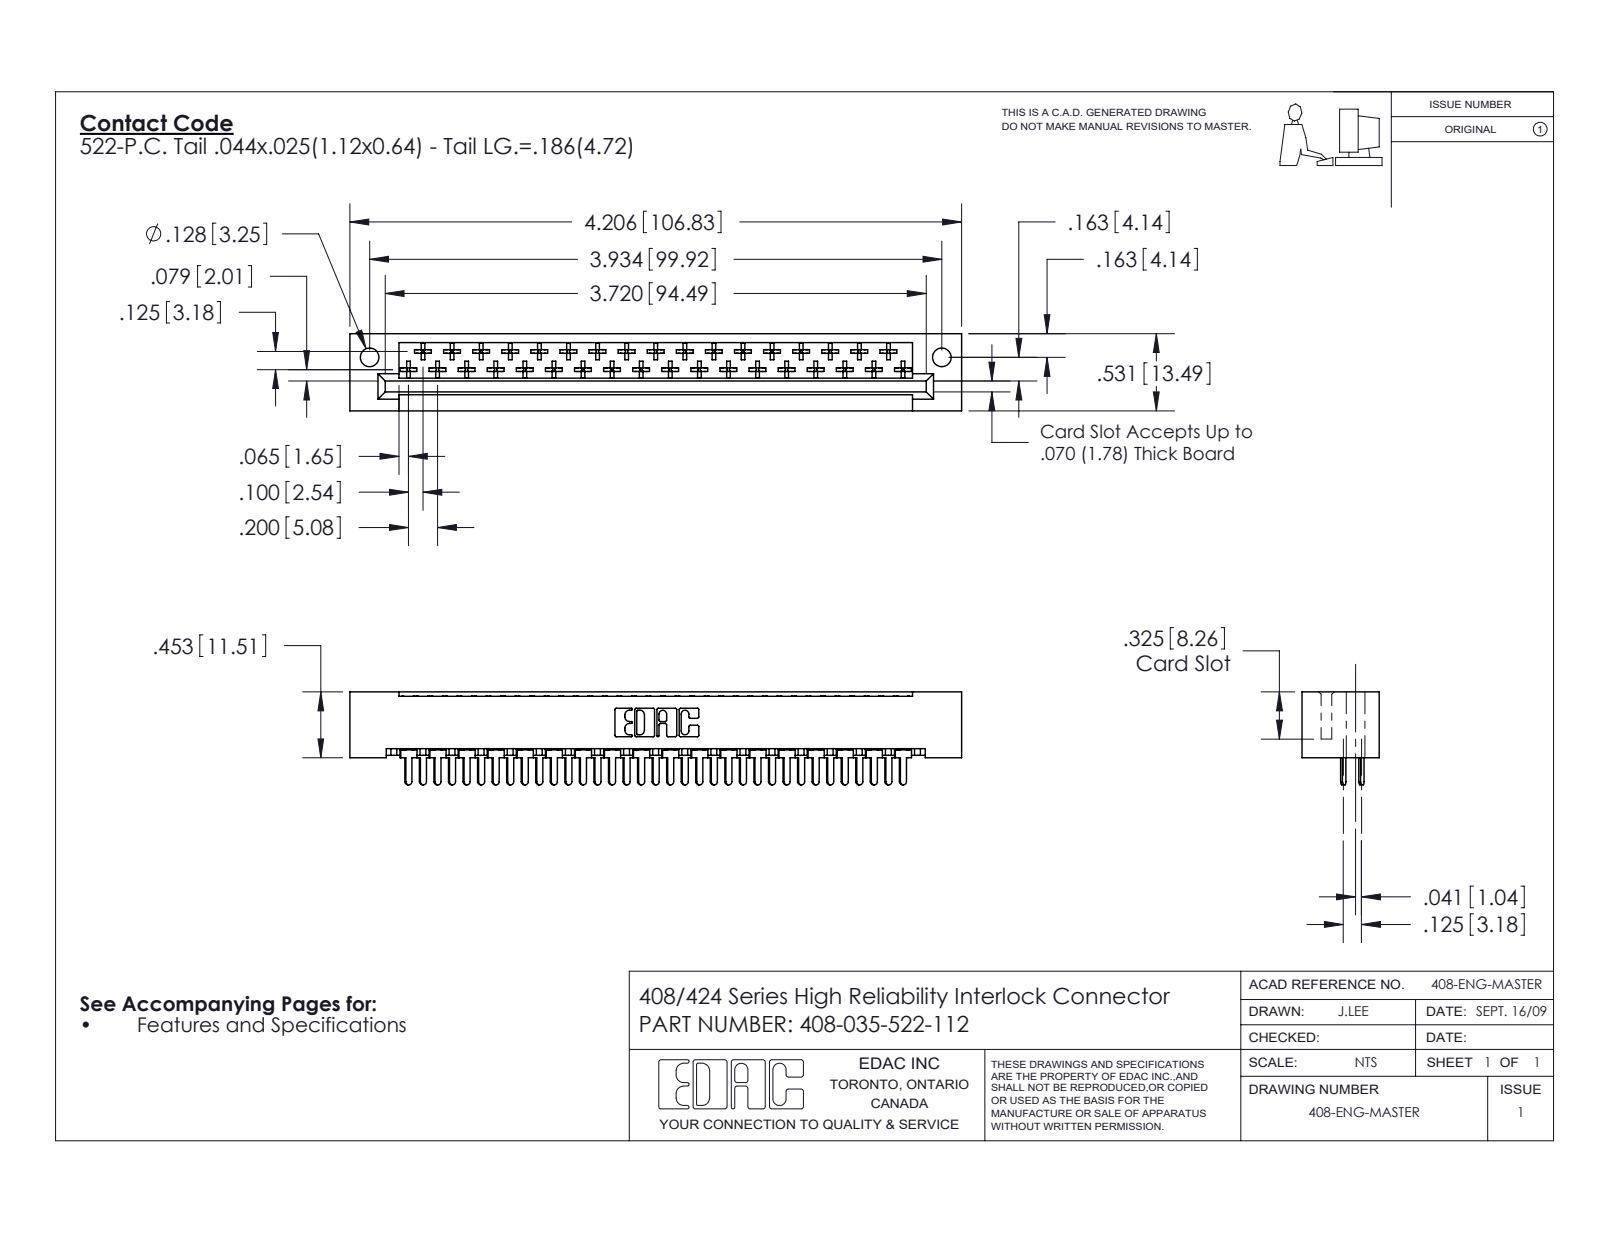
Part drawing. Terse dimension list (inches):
name: 408 Part_035 - 1; 408-035-522-112; 408-290-001_408-290-122
written by: SolidWorks 2016 (CONFIG_CONTROL_DESIGN)
unit: in
bodies: 36 solids, 2052 faces (1549 planar, 363 cylindrical, 140 other)
size: 4.206 × 0.639 × 0.531
volume: 0.748 in³; area: 22.65 in²
holes: 2× ⌀0.128
rounds: 210× R0.01, 37× R0.02, 35× R0.022, 22× R0.01, 6× R0.007, 6× R0.031, 3× R0.026
face distances: 0.531, 0.025, 0.1, 0.125, 0.025, 0.4, 0.272, 0.235, 0.259, 0.296
hole spacings: 3.934
